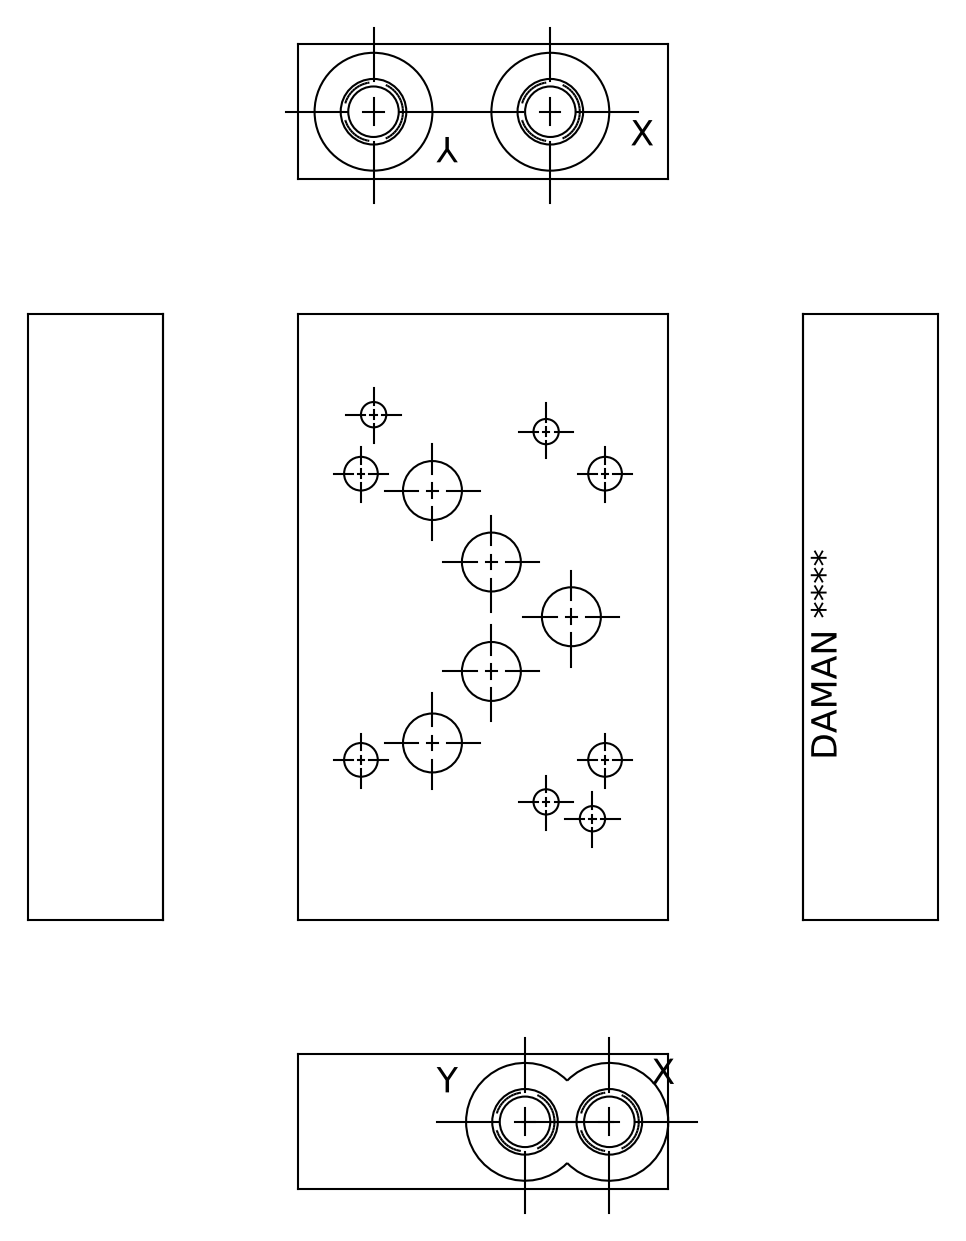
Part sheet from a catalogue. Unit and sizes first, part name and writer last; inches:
Units: inches
Overall size (bounding box): 4.5 × 2.75 × 1
Round holes (diameter × count): ⌀0.438 ×8, ⌀0.625 ×7, ⌀0.437 ×6, ⌀0.188 ×4, ⌀0.281 ×4, ⌀0.375 ×4, ⌀0.389 ×4, ⌀0.488 ×4, ⌀0.838 ×2
Partial cylindrical surfaces — rounded edges, fillets, slot ends (radius × count): R0.141 ×3, R0.419 ×2
Main face-to-face distances: 1, 2.75, 4.5, 0.052, 0.948, 0.031, 4.469, 4.438, 2.748, 0.484
Hole centre spacings: 0.688, 0.72, 0.72, 0.813, 0.813, 1.069, 1.413, 1.694
Volume: 11.32 in³ · Surface area: 48.77 in²
Bodies: 1 solid, 456 faces (317 planar, 49 cylindrical, 90 other)
Part name (STEP PRODUCT): Part_AD05HTPXY4S_3D
STEP written by: Autodesk Inventor 2022 (AUTOMOTIVE_DESIGN)
